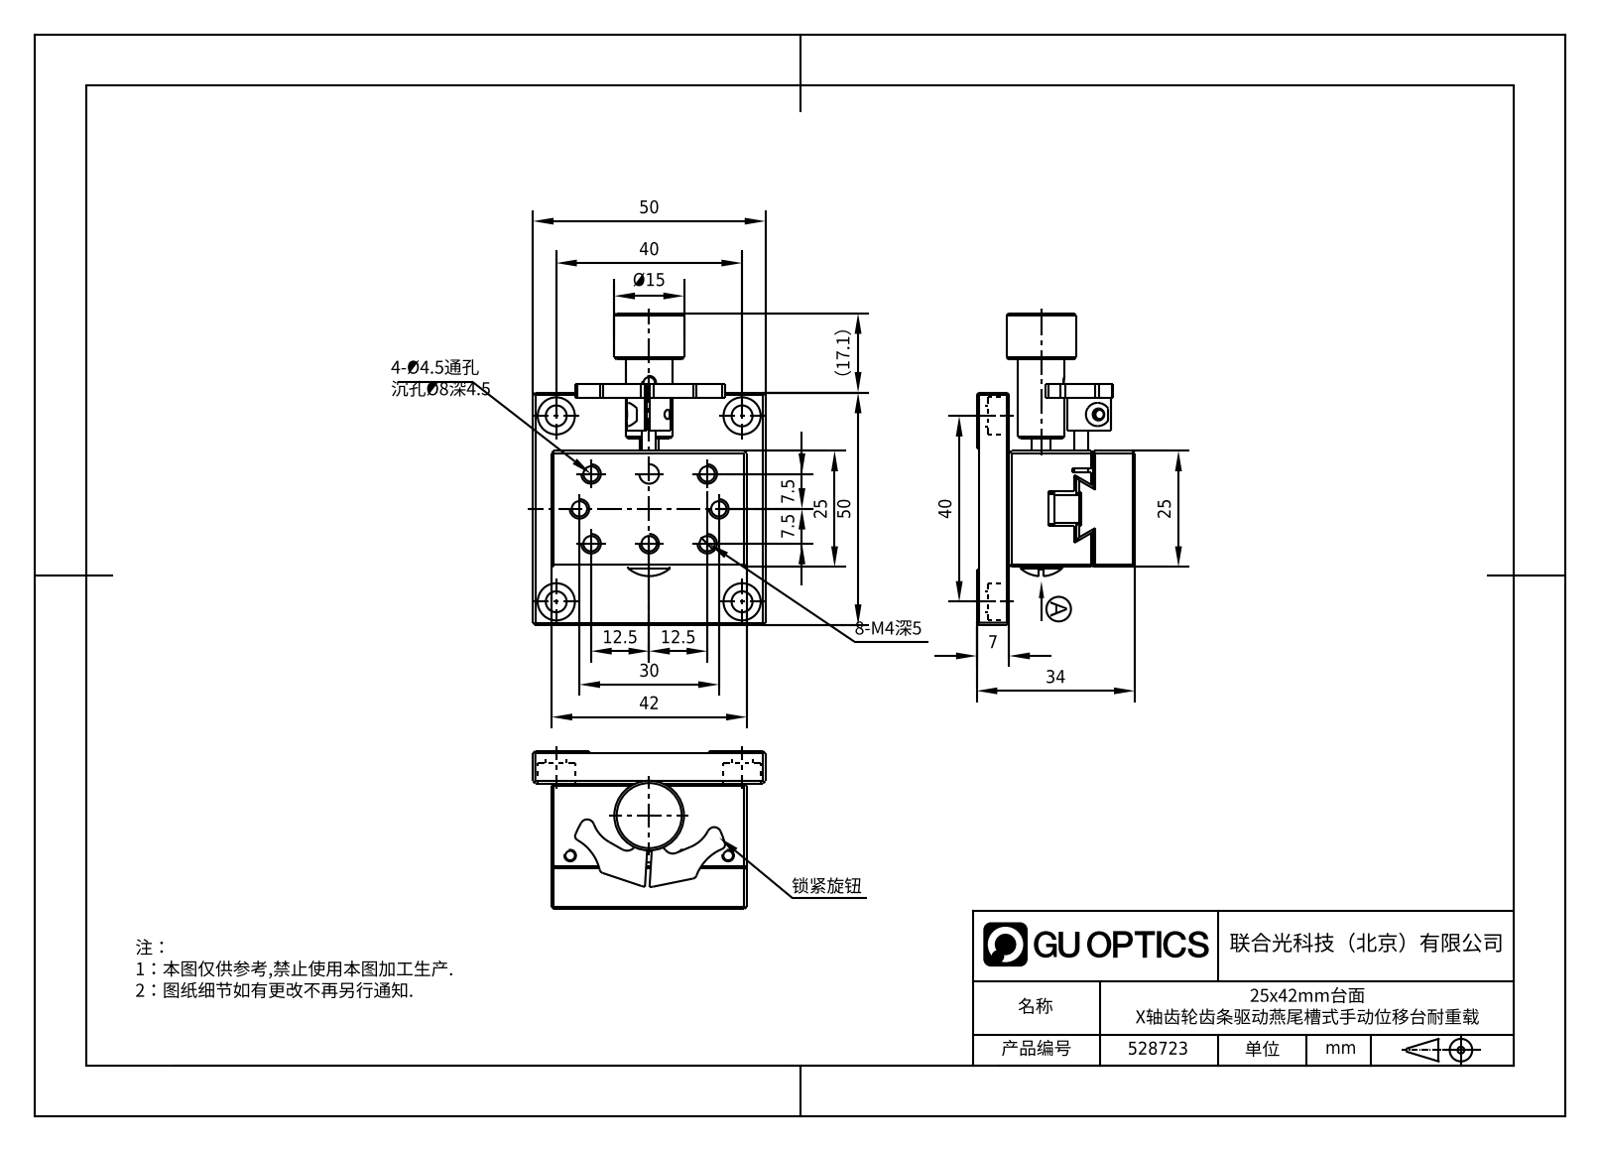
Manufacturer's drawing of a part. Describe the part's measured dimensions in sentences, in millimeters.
The part is named "528723". Its 3-D file was written by "SolidWorks 2020 (CONFIG_CONTROL_DESIGN)". It is 6 solids with 550 faces: 275 planar, 125 cylindrical and 150 other. Overall it measures 67.1 by 50 by 34 millimeters. Its volume is 45 463 cubic millimeters and its surface area 22 325 square millimeters. Round holes: 10 of diameter 3.24, 6 of diameter 4.5, 4 of diameter 8, 3 of diameter 2.01, 3 of diameter 2.01, 3 of diameter 5, 2 of diameter 2.46, 2 of diameter 2.8, 2 of diameter 7.5, 1 of diameter 2.5, 1 of diameter 2.6, 1 of diameter 3.3. Round bosses or shafts: 1 of diameter 10, 1 of diameter 9, 1 of diameter 8, 1 of diameter 6.5, 1 of diameter 5.83, 1 of diameter 3. Partial cylindrical surfaces (rounded edges, fillets, slot ends): 4 of radius 1, 2 of radius 1.5, 2 of radius 2, 2 of radius 7.6, 2 of radius 10, 1 of radius 4.7, 1 of radius 5, 1 of radius 7.5. The main face-to-face distances are 6.5, 25, 0.5, 4, 22, 24.5, 18, 12.5, 27, 21.5. The hole center spacings are 34, 23.58, 28.5, 7.91, 8.75, 9.01, 10.61, 12.5.
